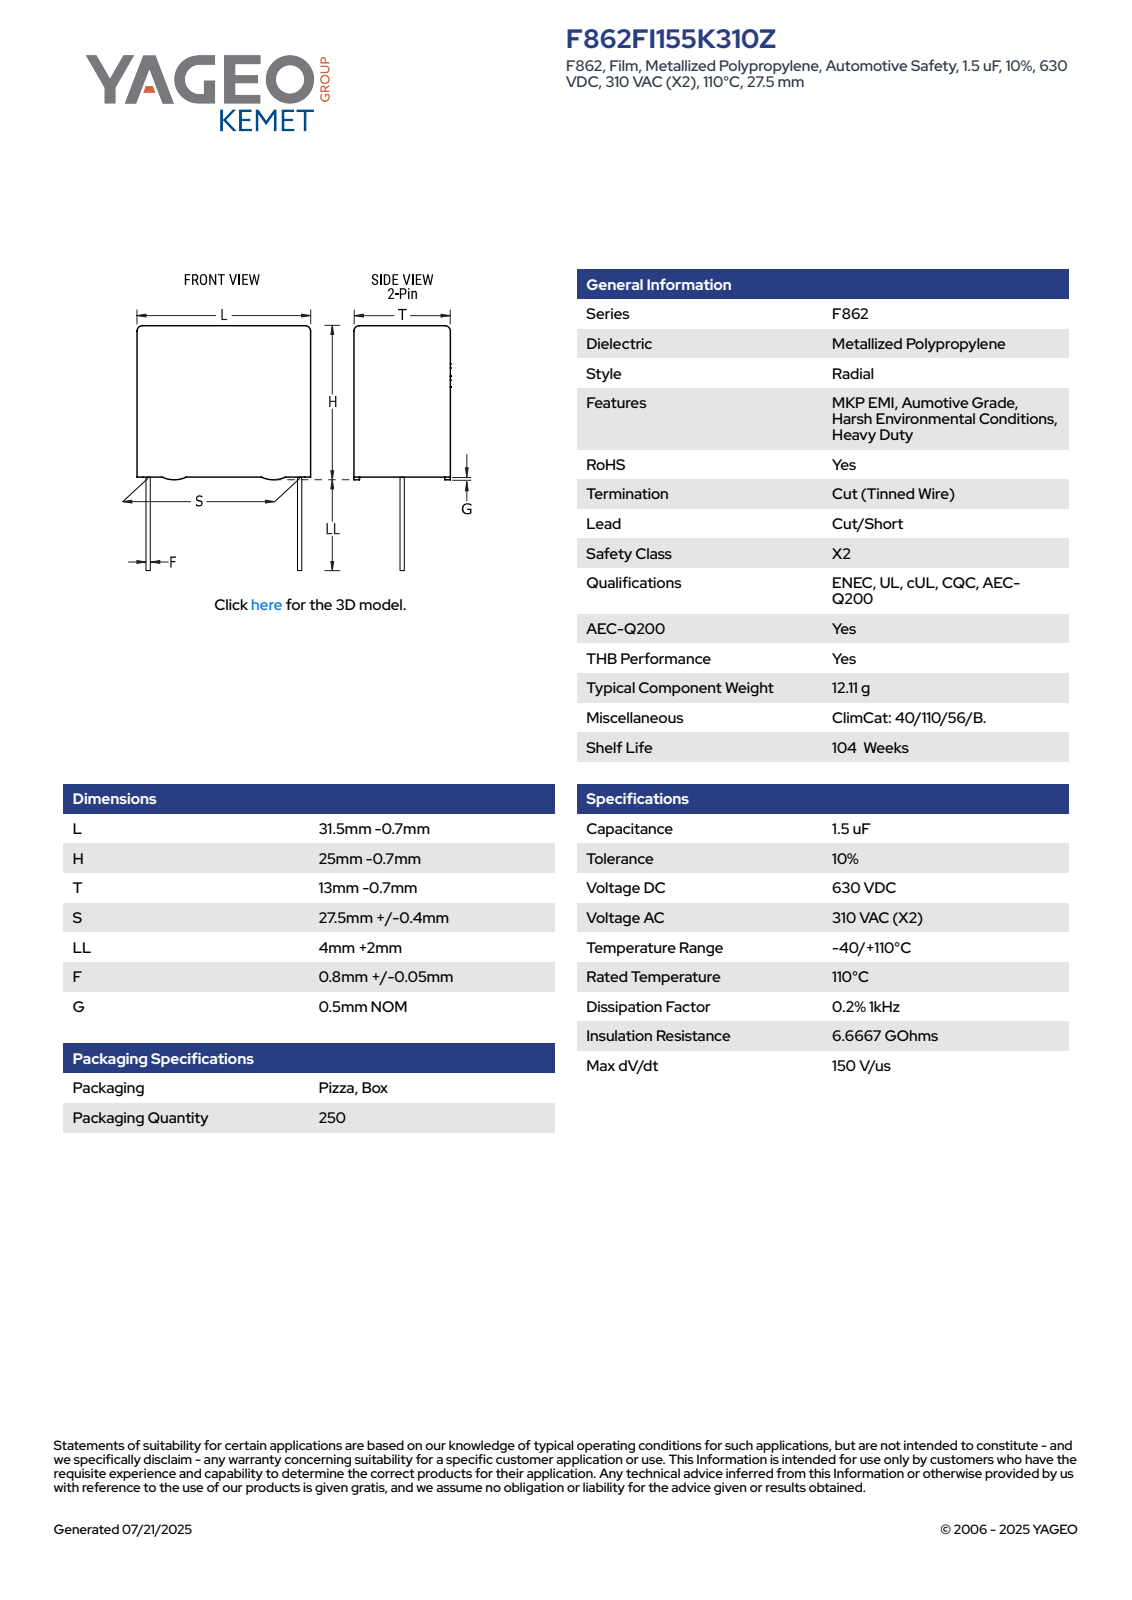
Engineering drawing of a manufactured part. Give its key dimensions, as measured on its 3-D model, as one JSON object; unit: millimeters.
{"part_name": "CFR_RBG_31.5X25X13_L30.8H24.3T12.3S27.5LL6F0.85G0.5", "step_written_by": "SolidWorks 2014 (AUTOMOTIVE_DESIGN)", "units": "millimeters", "bodies": {"solids": 4, "faces": 89, "planar": 81, "cylindrical": 8, "other": 0}, "overall_size": [30.8, 30.3, 12.3], "volume_mm3": 9026, "surface_area_mm2": 2949, "round_bosses_or_shafts": [[0.85, 2]], "partial_cylinders_radius": [[0.5, 4]], "face_to_face_distances": [12.3, 23.8, 30.8, 0.5, 24.3, 0.7, 11.6, 10.9, 6, 6.5]}
